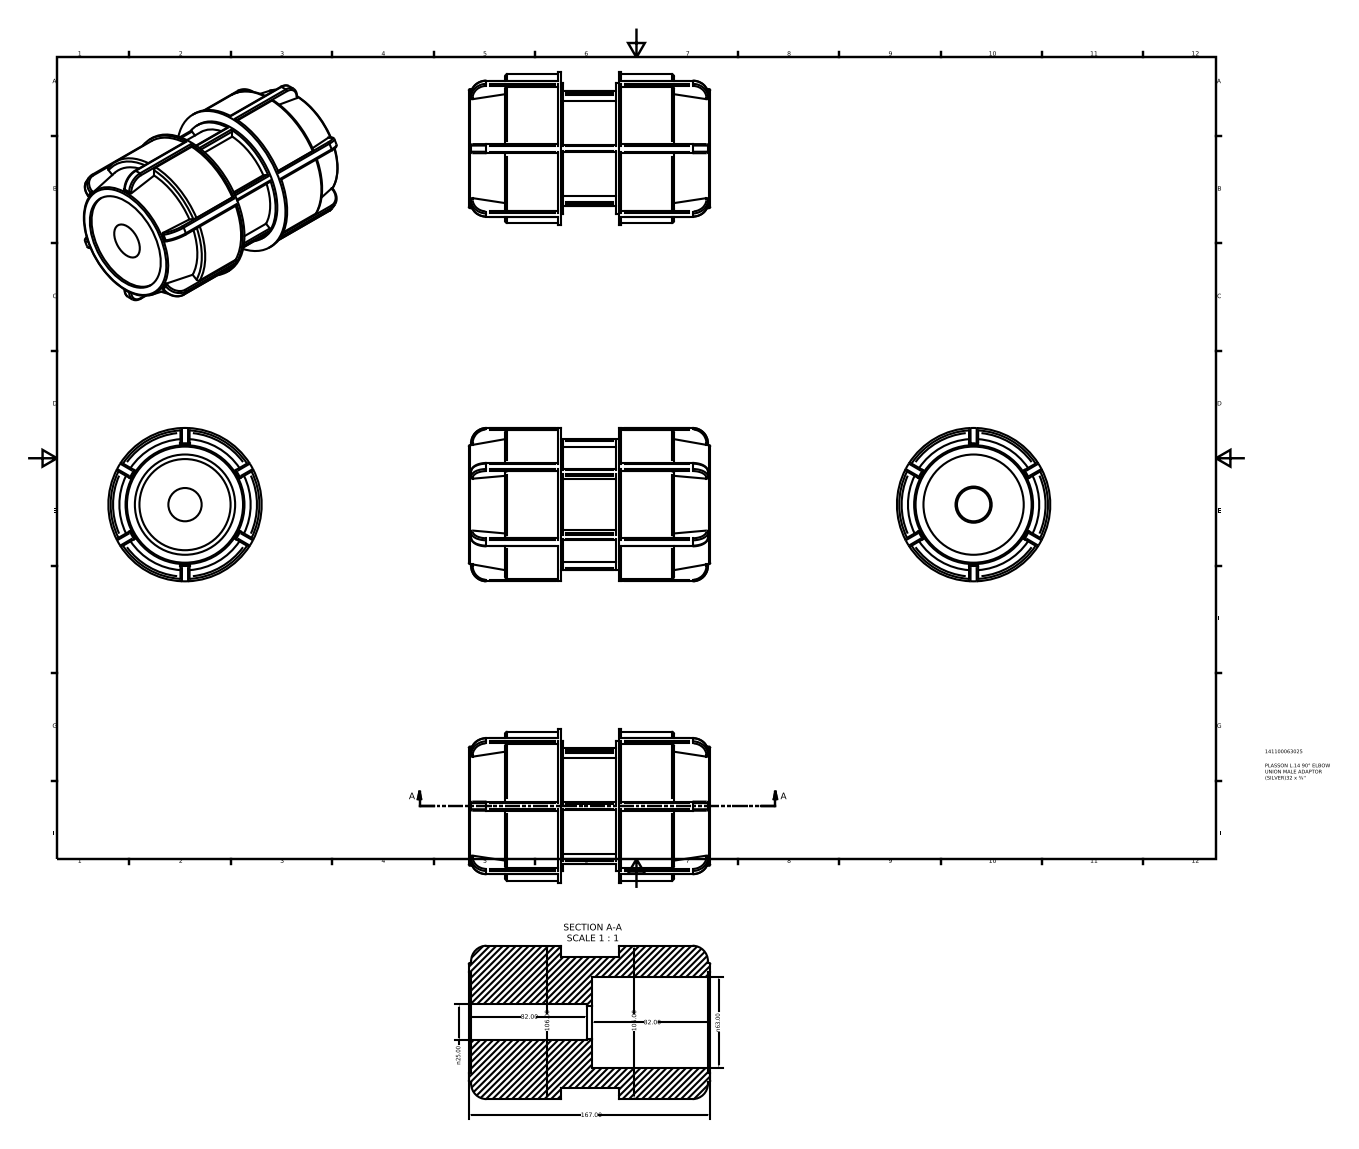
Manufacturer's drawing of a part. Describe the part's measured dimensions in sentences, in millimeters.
The part is named "141100063025". Its 3-D file was written by "Autodesk Inventor 2015 (AUTOMOTIVE_DESIGN)". It is 1 solid with 230 faces: 92 planar, 86 cylindrical and 52 other. Overall it measures 167 by 106 by 106 millimeters. Its volume is 858 083 cubic millimeters and its surface area 100 908 square millimeters. Round holes: 1 of diameter 23, 1 of diameter 25, 1 of diameter 63, 1 of diameter 69.3. Round bosses or shafts: 1 of diameter 106, 1 of diameter 102.82, 1 of diameter 90.1, 1 of diameter 79.5. Partial cylindrical surfaces (rounded edges, fillets, slot ends): 44 of radius 1.06. The main face-to-face distances are 40.08, 101.87, 1.67, 38.41, 63.46, 61.79, 103.54, 83.33, 18.54, 21.54.
